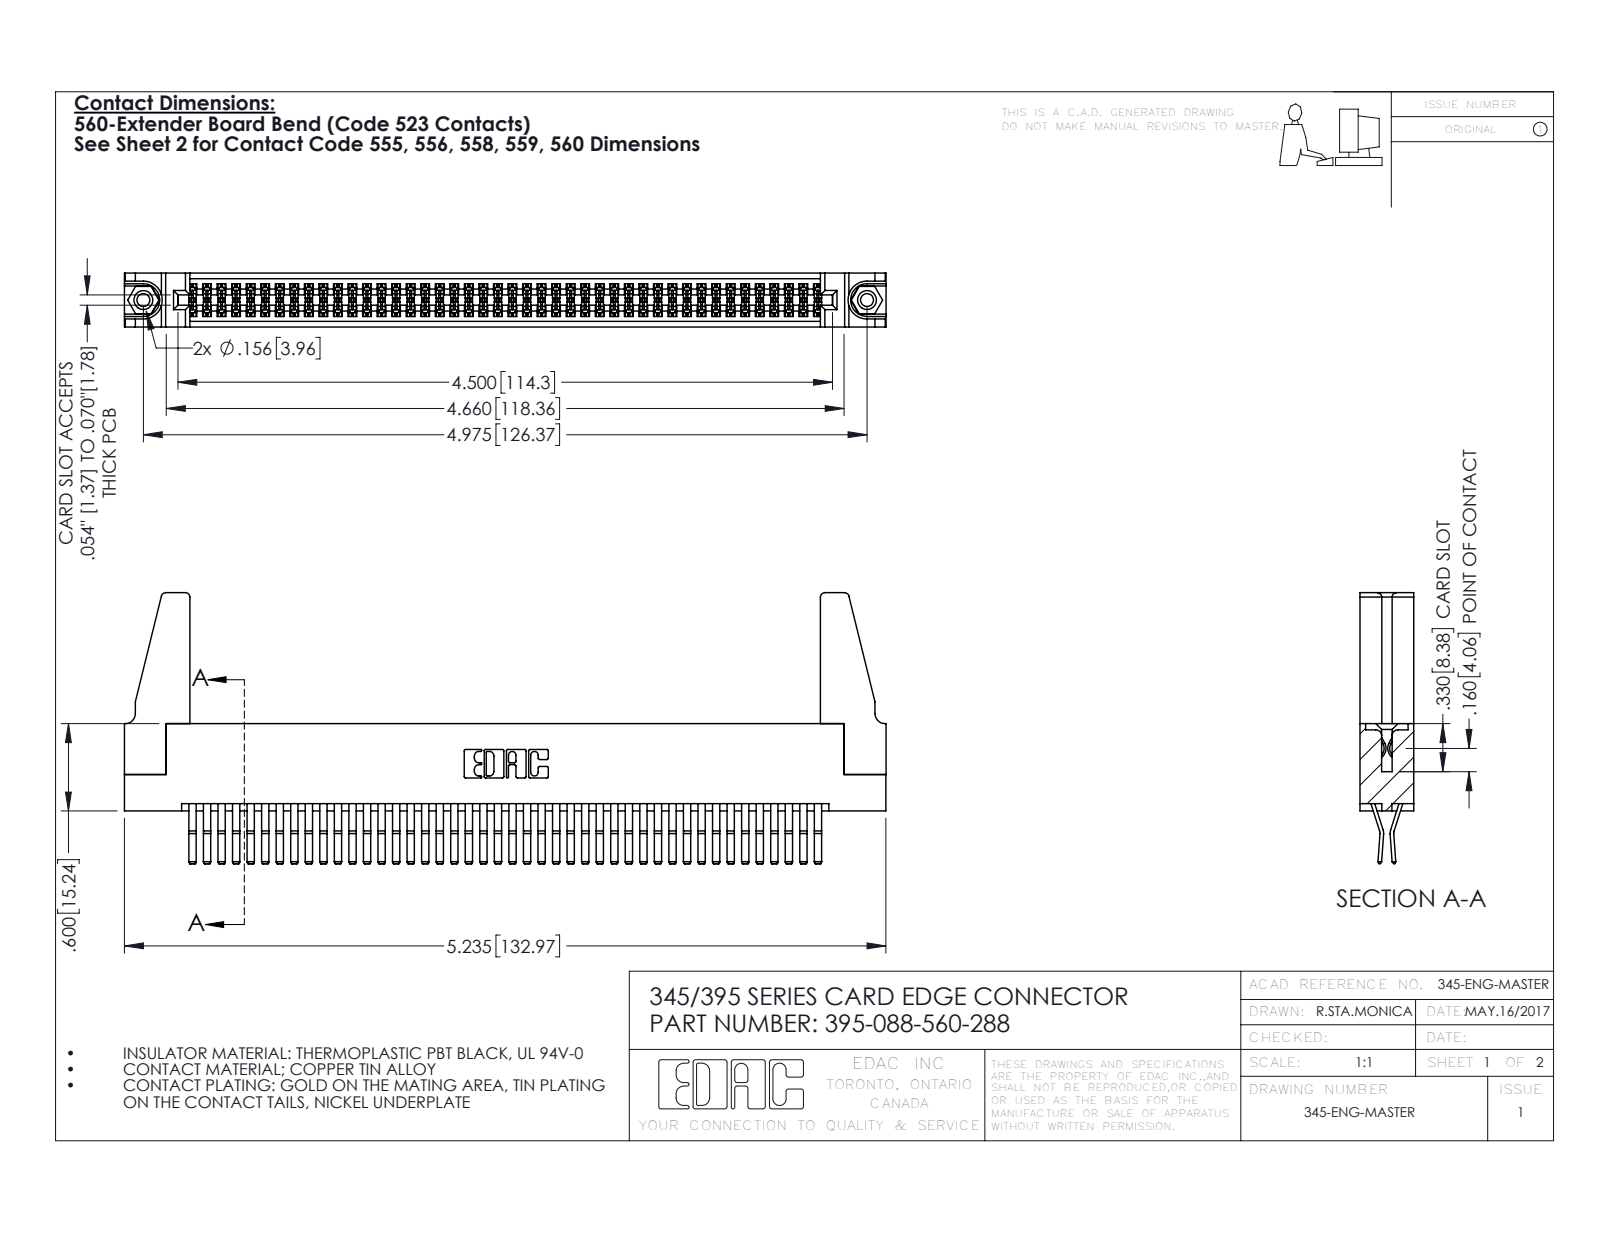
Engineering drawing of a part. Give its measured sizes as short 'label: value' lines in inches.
name: 395-088-560-288; 345-220-078_345-220-088; 345-292-001_560 Tail; 345 Part_Flush Mounting Lugs - 0.156 Dia-TH (+1 more)
written by: SolidWorks 2016 (CONFIG_CONTROL_DESIGN)
unit: in
bodies: 93 solids, 4826 faces (3056 planar, 1754 cylindrical, 16 other)
size: 5.236 × 1.862 × 0.37
volume: 1.023 in³; area: 38.16 in²
holes: 2× ⌀0.089, 2× ⌀0.125, 2× ⌀0.156, 1× ⌀0.064
bosses: 2× ⌀0.155
rounds: 132× R0.006, 22× R0.01, 8× R0.03, 6× R0.007, 6× R0.031, 3× R0.026, 2× R0.01, 2× R0.014
face distances: 0.072, 0.298, 0.025, 0.37, 0.2, 0.098, 0.272, 0.225, 0.175, 0.149
hole spacings: 0.27, 4.739, 4.975
